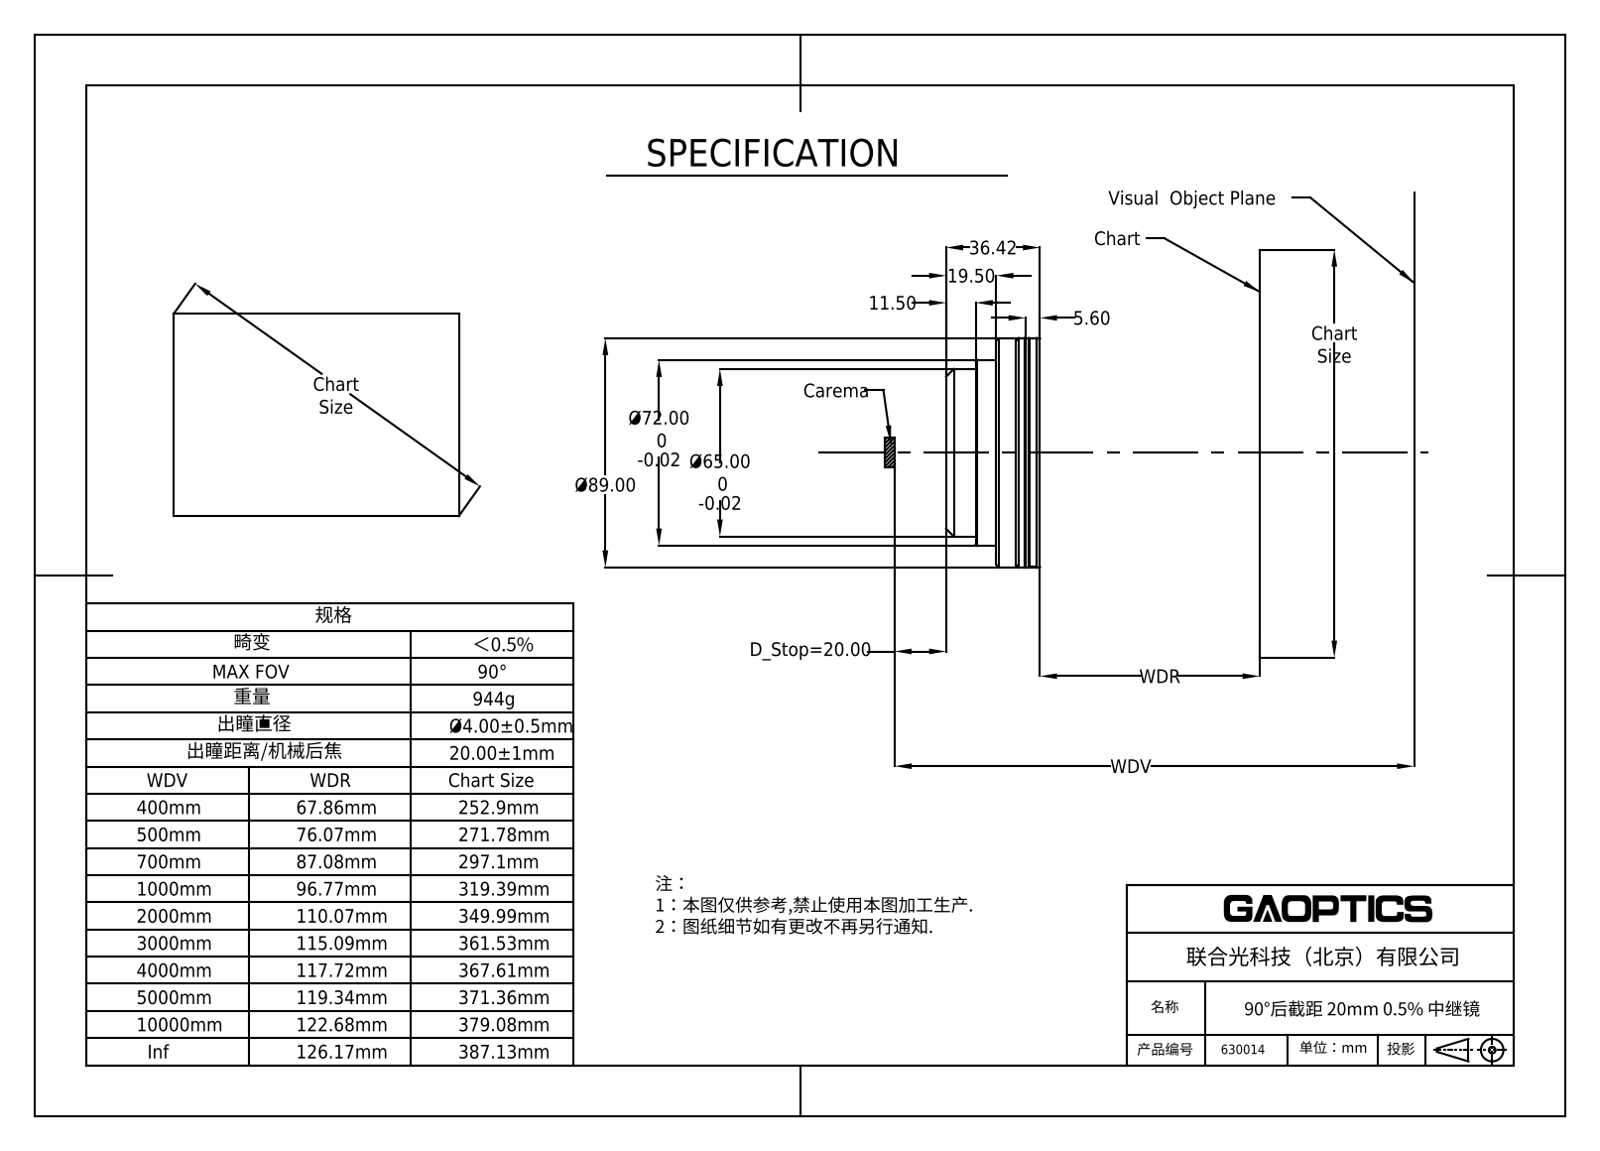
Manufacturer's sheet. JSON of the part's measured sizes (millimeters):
{"part_name": "630014", "step_written_by": "SolidWorks 2020 (CONFIG_CONTROL_DESIGN)", "units": "millimeters", "bodies": {"solids": 1, "faces": 77, "planar": 11, "cylindrical": 28, "other": 38}, "overall_size": [130, 130, 55.5], "volume_mm3": 422716, "surface_area_mm2": 43222, "round_holes": [[3.4, 4], [6, 4], [98, 1]], "round_bosses_or_shafts": [[130, 1], [110, 1], [85, 1], [62, 1]], "face_to_face_distances": [10, 13, 23, 12.5, 25.5, 35.5, 8.5, 21, 34, 44], "hole_center_spacings": [60, 84.85, 120]}
